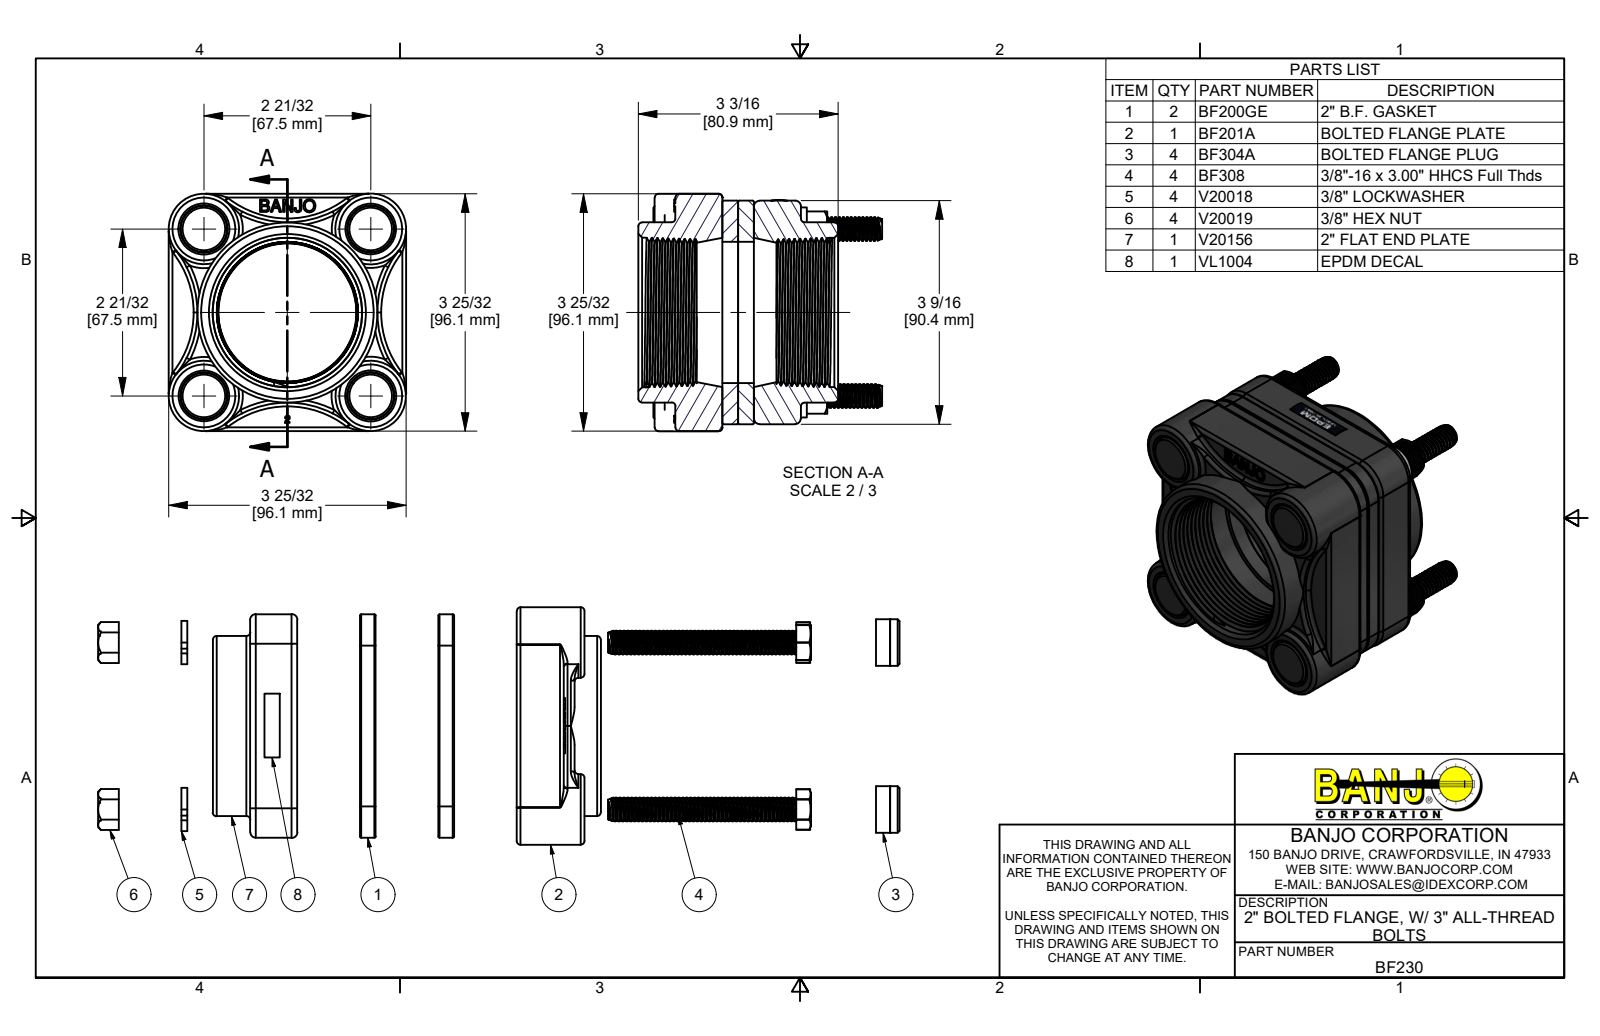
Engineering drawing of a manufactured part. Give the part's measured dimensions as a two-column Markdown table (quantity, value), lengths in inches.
| quantity | value |
| --- | --- |
| part name | BF230; BF200GE; BF201A; BF304A (+5 more) |
| STEP written by | Autodesk Inventor 2019 (AUTOMOTIVE_DESIGN) |
| units | inches |
| bodies | 21 solids, 1628 faces (311 planar, 602 cylindrical, 715 other) |
| overall size | 39.053 × 3.784 × 3.784 |
| volume | 22.42 in³ |
| surface area | 465.6 in² |
| round holes (diameter × count) | 0.307 × 4, 0.38 × 4, 0.385 × 4, 0.406 × 4, 0.41 × 4, 0.715 × 4, 0.75 × 4, 2.25 × 1 |
| round bosses / shafts (diameter × count) | 0.324 × 188, 1.125 × 4, 0.742 × 4, 0.687 × 4, 0.375 × 4, 2.87 × 1 |
| partial cylindrical surfaces (radius × count) | 0.02 × 16, 0.06 × 16, 0.09 × 8, 0.162 × 8, 0.322 × 4, 0.47 × 4, 0.5 × 4, 1.6 × 4 |
| main face-to-face distances | 0.25, 0.5, 0.111, 3.671, 0.75, 1, 1.25, 3.56, 3.782, 1.344 |
| hole center spacings | 1.88, 2.659, 3.761 |
